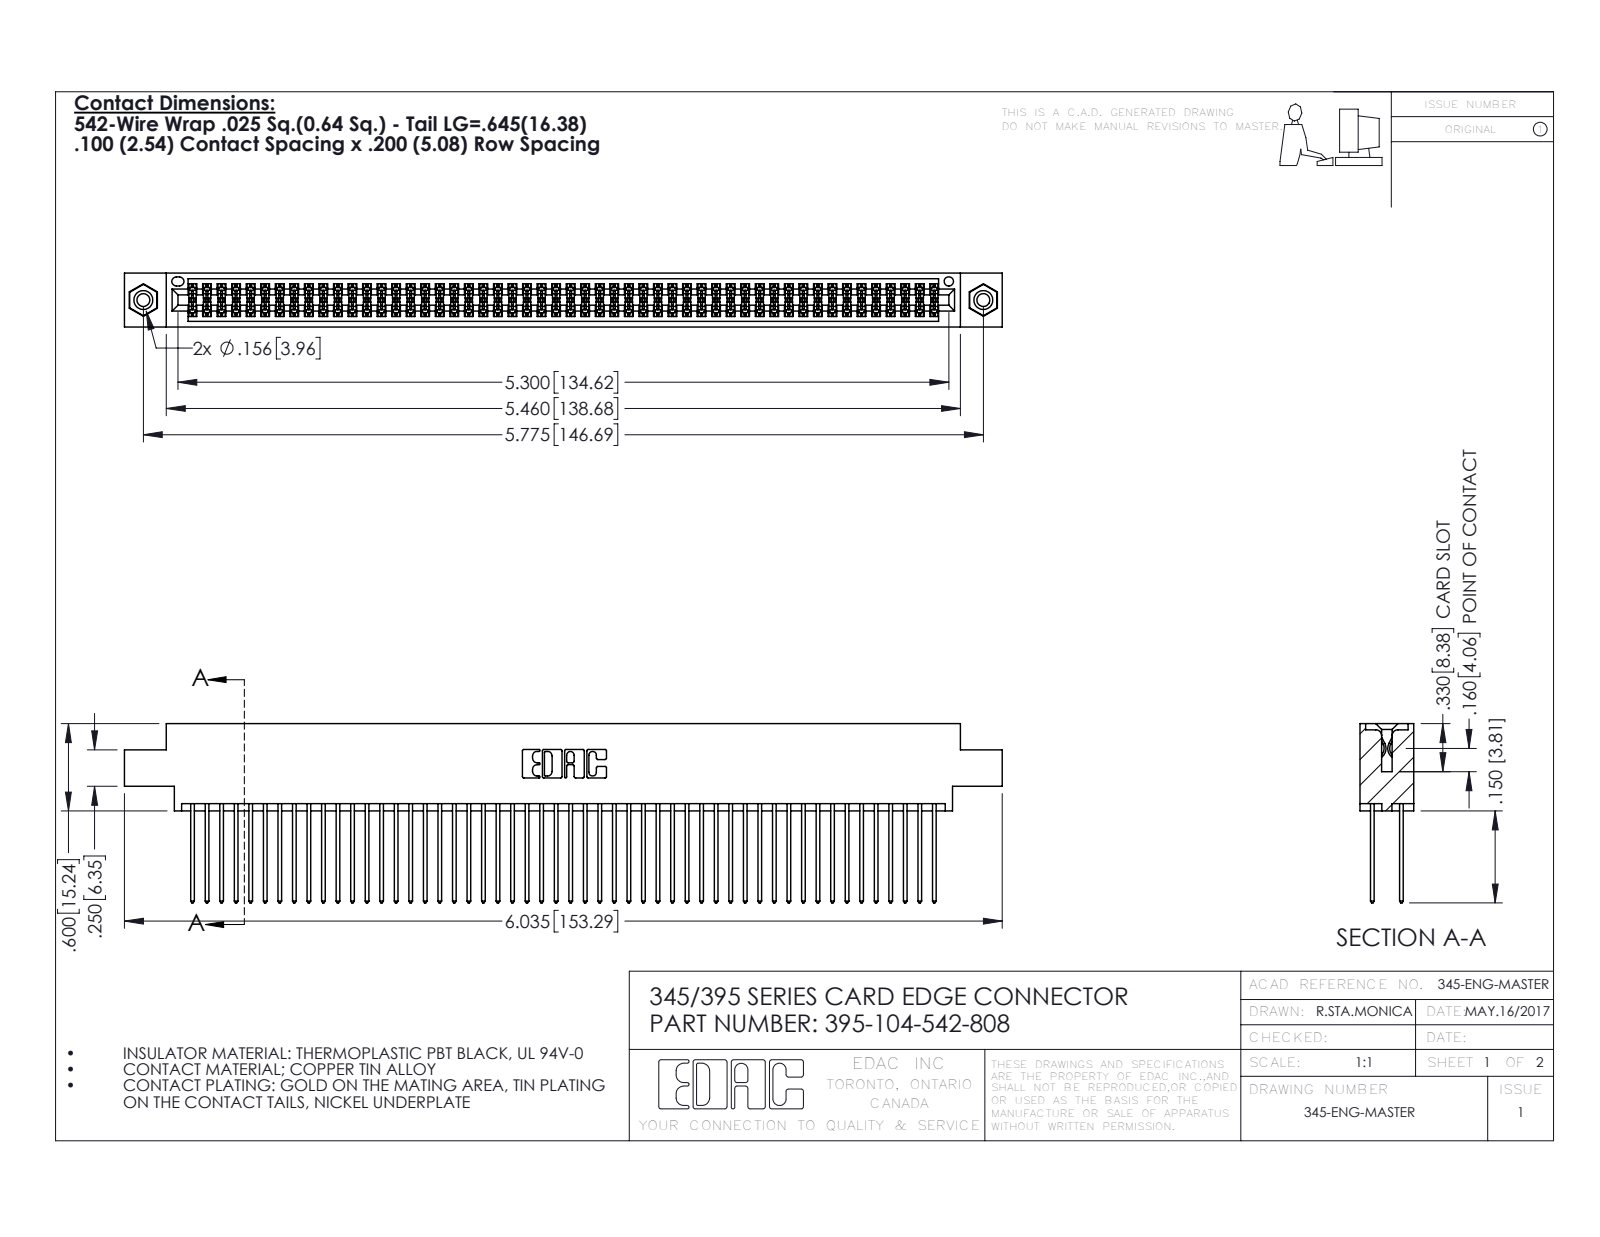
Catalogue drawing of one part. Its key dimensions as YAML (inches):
part_name: "345-250-001_345-250-003-102; 345 Part_0.170 Offset - 0.156 Dia-TI; 395-104-542-808; 345-292-001_345-293-142"
step_written_by: "SolidWorks 2016 (CONFIG_CONTROL_DESIGN)"
units: inches
bodies: {solids: 107, faces: 5390, planar: 3548, cylindrical: 1826, other: 16}
overall_size: [6.035, 1.232, 0.37]
volume: 0.937
surface_area: 39.22
round_holes:
  - {diameter: 0.089, count: 2}
  - {diameter: 0.125, count: 2}
  - {diameter: 0.156, count: 2}
  - {diameter: 0.064, count: 1}
round_bosses_or_shafts:
  - {diameter: 0.155, count: 2}
partial_cylinders:
  - {radius: 0.006, count: 156}
  - {radius: 0.01, count: 104}
  - {radius: 0.01, count: 22}
  - {radius: 0.007, count: 6}
  - {radius: 0.031, count: 6}
  - {radius: 0.026, count: 3}
  - {radius: 0.014, count: 2}
  - {radius: 0.019, count: 2}
face_to_face_distances: [0.072, 0.298, 0.2, 0.098, 0.272, 0.025, 0.37, 0.225, 0.175, 0.149]
hole_center_spacings: [0.27, 5.539, 5.775]
